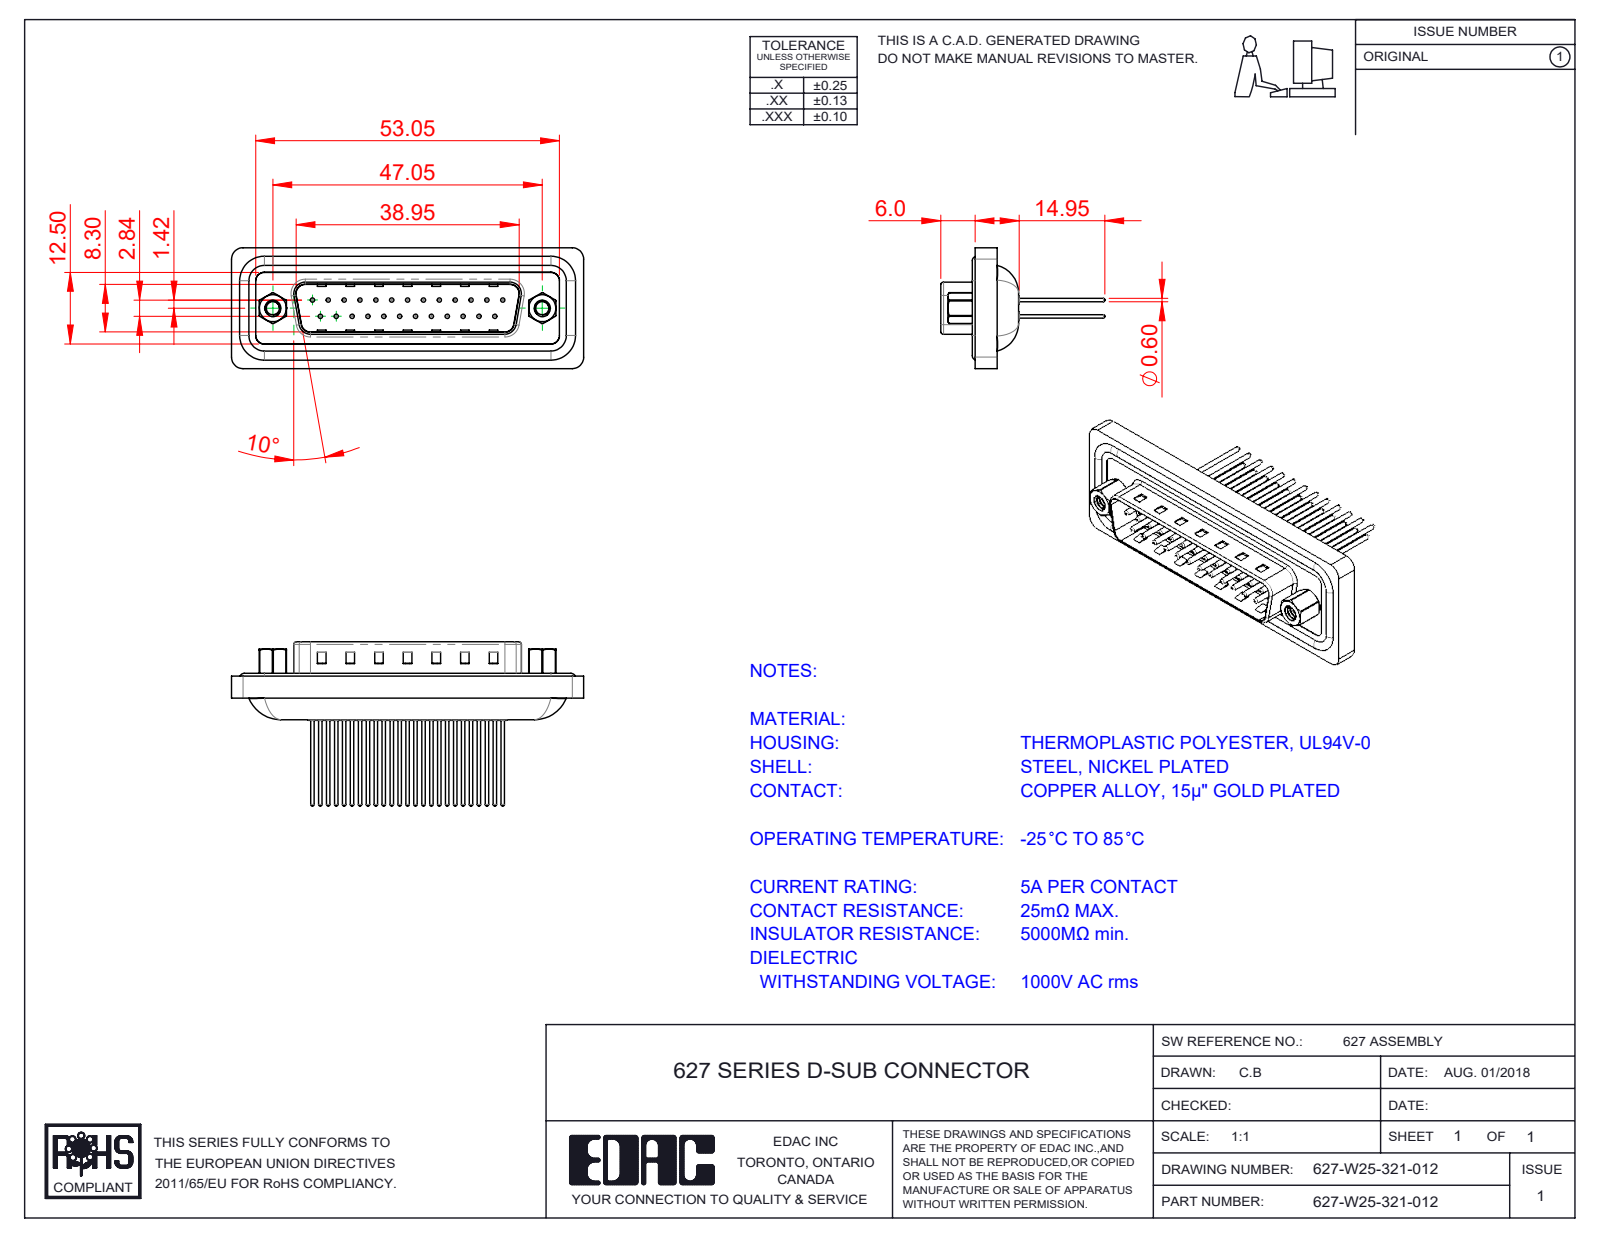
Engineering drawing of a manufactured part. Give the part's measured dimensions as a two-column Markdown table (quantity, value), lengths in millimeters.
| quantity | value |
| --- | --- |
| part name | 627W Waterproof Housing_25 Contacts; 627W 4-40 Threaded Rivet; 627W Contact Row 1_21; 627W Contact Row 2_21 (+4 more) |
| STEP written by | SolidWorks 2023 (CONFIG_CONTROL_DESIGN) |
| units | millimeters |
| bodies | 33 solids, 1495 faces (380 planar, 620 cylindrical, 495 other) |
| overall size | 61.5 × 28.85 × 21.1 |
| volume | 7 552 mm³ |
| surface area | 11 602 mm² |
| round holes (diameter × count) | 0.75 × 25, 1.5 × 25, 1.6 × 25, 2 × 25, 2.26 × 2, 2.29 × 2, 4 × 2, 4.8 × 2, 5 × 2 |
| round bosses / shafts (diameter × count) | 0.6 × 25, 1.5 × 7, 1.6 × 4, 4.9 × 2, 2.79 × 2 |
| partial cylindrical surfaces (radius × count) | 2 × 16, 1.5 × 14, 0.5 × 8, 2.7 × 6, 0.9 × 4, 1.6 × 4, 4.3 × 4, 0.4 × 2 |
| main face-to-face distances | 0.75, 0.4, 1.1, 2.75, 4.6, 3.75, 4.1, 0.5, 5.65, 15.45 |
| hole center spacings | 3.16, 2.77, 5.54, 8.31, 11.08, 13.85, 5.04, 16.62 |
